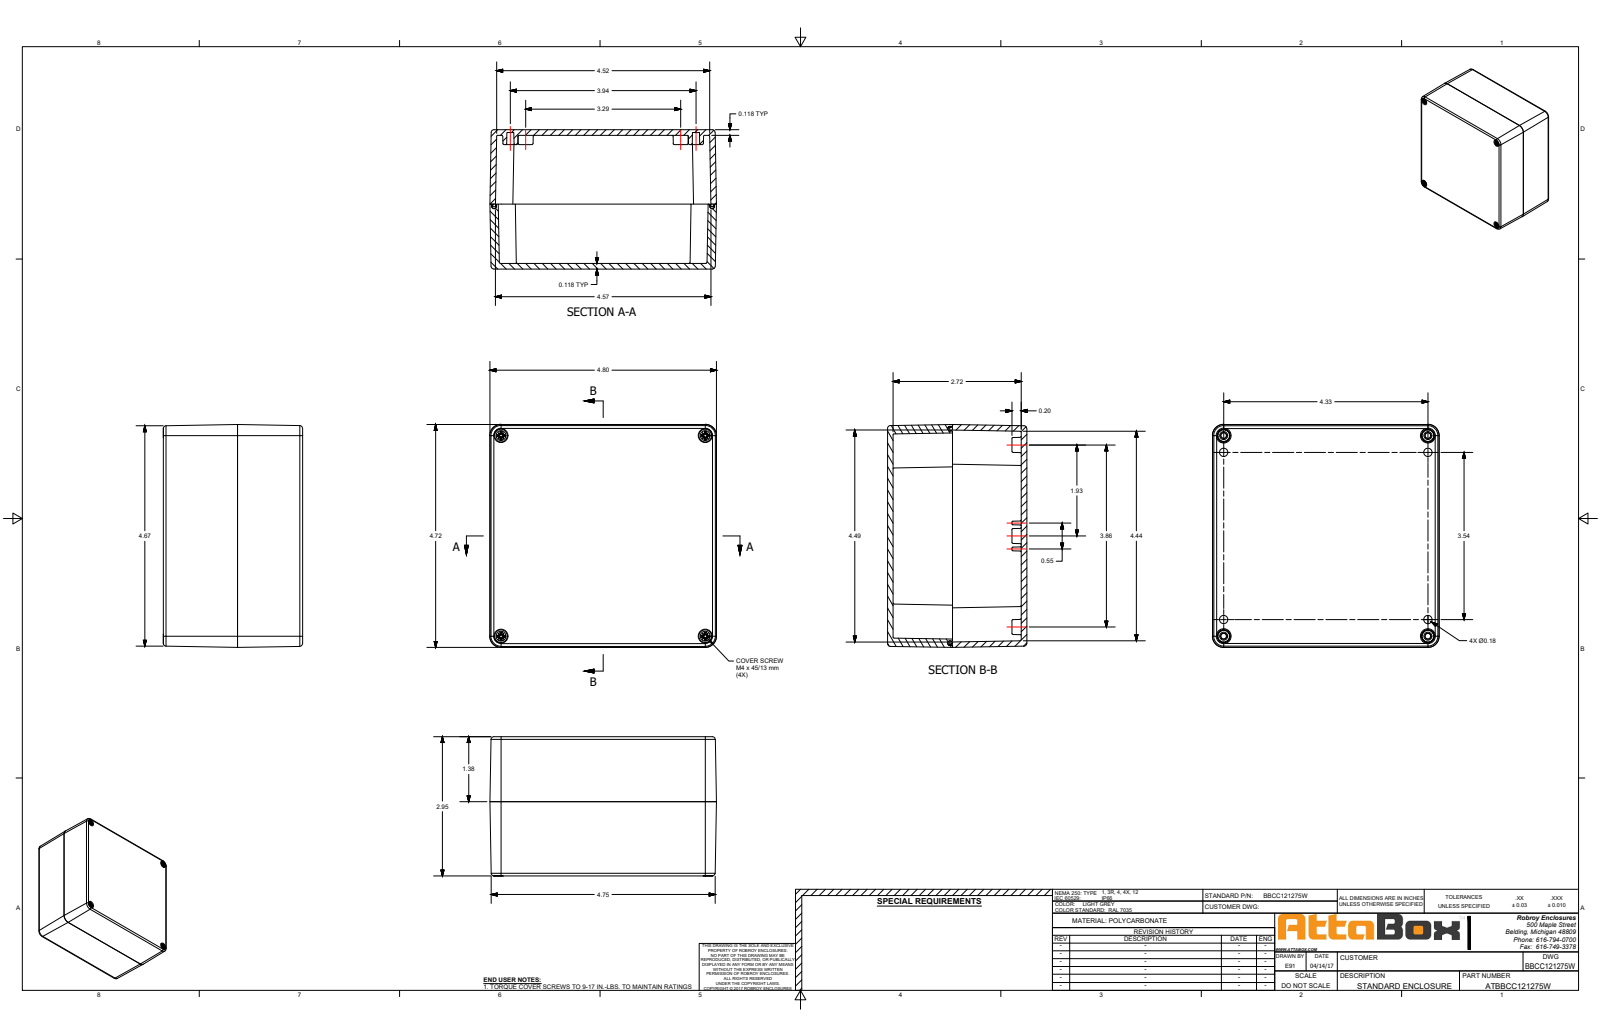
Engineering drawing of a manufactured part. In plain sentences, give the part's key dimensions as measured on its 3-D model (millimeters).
The part is named "BBCC121275W". Its 3-D file was written by "SolidWorks 2018 (AUTOMOTIVE_DESIGN)". It is 11 solids with 1669 faces: 611 planar, 440 cylindrical and 618 other. Overall it measures 122 by 120 by 75 millimeters. Its volume is 224 800 cubic millimeters and its surface area 149 000 square millimeters. Round holes: 8 of diameter 4.5, 4 of diameter 3.3, 4 of diameter 4.8, 4 of diameter 5.1, 4 of diameter 7, 4 of diameter 7.5, 4 of diameter 8. Round bosses or shafts: 4 of diameter 6.8, 4 of diameter 4.4, 4 of diameter 4, 4 of diameter 3.3. Partial cylindrical surfaces (rounded edges, fillets, slot ends): 48 of radius 1, 40 of radius 0.5, 12 of radius 5, 8 of radius 1.5, 8 of radius 2.5, 4 of radius 2.6, 4 of radius 3.1, 4 of radius 3.3. The main face-to-face distances are 3, 72, 75, 69, 4.5, 120, 122, 2.9, 117, 115.5. The hole center spacings are 9, 99, 110, 110.4, 148, 90, 108, 142.1.
